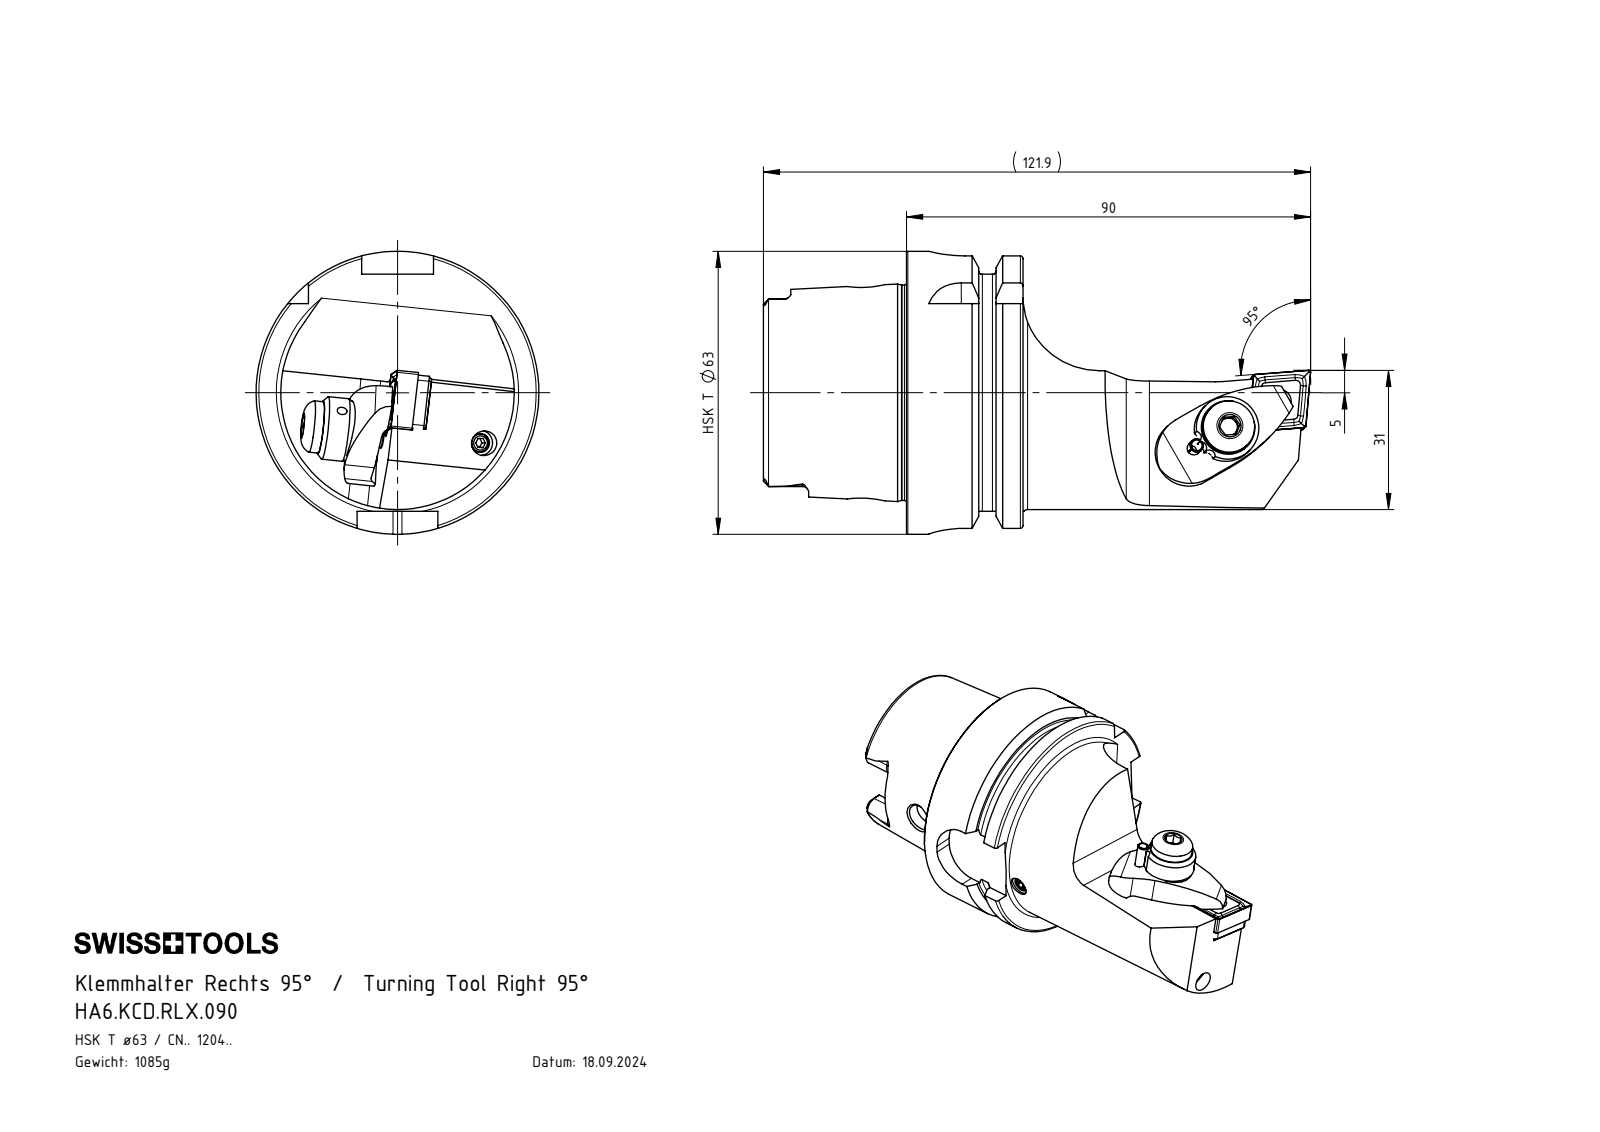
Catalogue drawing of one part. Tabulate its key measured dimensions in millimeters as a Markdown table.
| quantity | value |
| --- | --- |
| part name | ISO 13337 - 3 x 12_PreviewCfg; WCC-ER2.001.010_A; CNMG120404; WCC-ER3.102.024_C (+6 more) |
| STEP written by | SolidWorks 2022 (AUTOMOTIVE_DESIGN) |
| units | millimeters |
| bodies | 10 solids, 468 faces (142 planar, 155 cylindrical, 171 other) |
| overall size | 121.9 × 63 × 63 |
| volume | 137 533 mm³ |
| surface area | 35 430 mm² |
| round holes (diameter × count) | 4.2 × 4, 2 × 3, 5.5 × 2, 7 × 2, 8.5 × 2, 2.4 × 1, 3 × 1, 5 × 1, 5.16 × 1, 6.2 × 1, 6.55 × 1, 7.5 × 1 |
| round bosses / shafts (diameter × count) | 5 × 3, 3 × 2, 63 × 1, 54.95 × 1, 47.94 × 1, 14 × 1, 11.5 × 1, 7 × 1 |
| partial cylindrical surfaces (radius × count) | 0.39 × 6, 0.69 × 6, 1.4 × 6, 0.4 × 4, 1 × 4, 2.88 × 4, 8 × 4, 1.5 × 3 |
| main face-to-face distances | 25.95, 16, 9.95, 31.9, 41.85, 57.85, 52.8, 21.8, 11.85, 53.7 |
| hole center spacings | 7.99, 8.01, 8.2, 15.15, 22.94, 23, 7.15, 7.32 |
